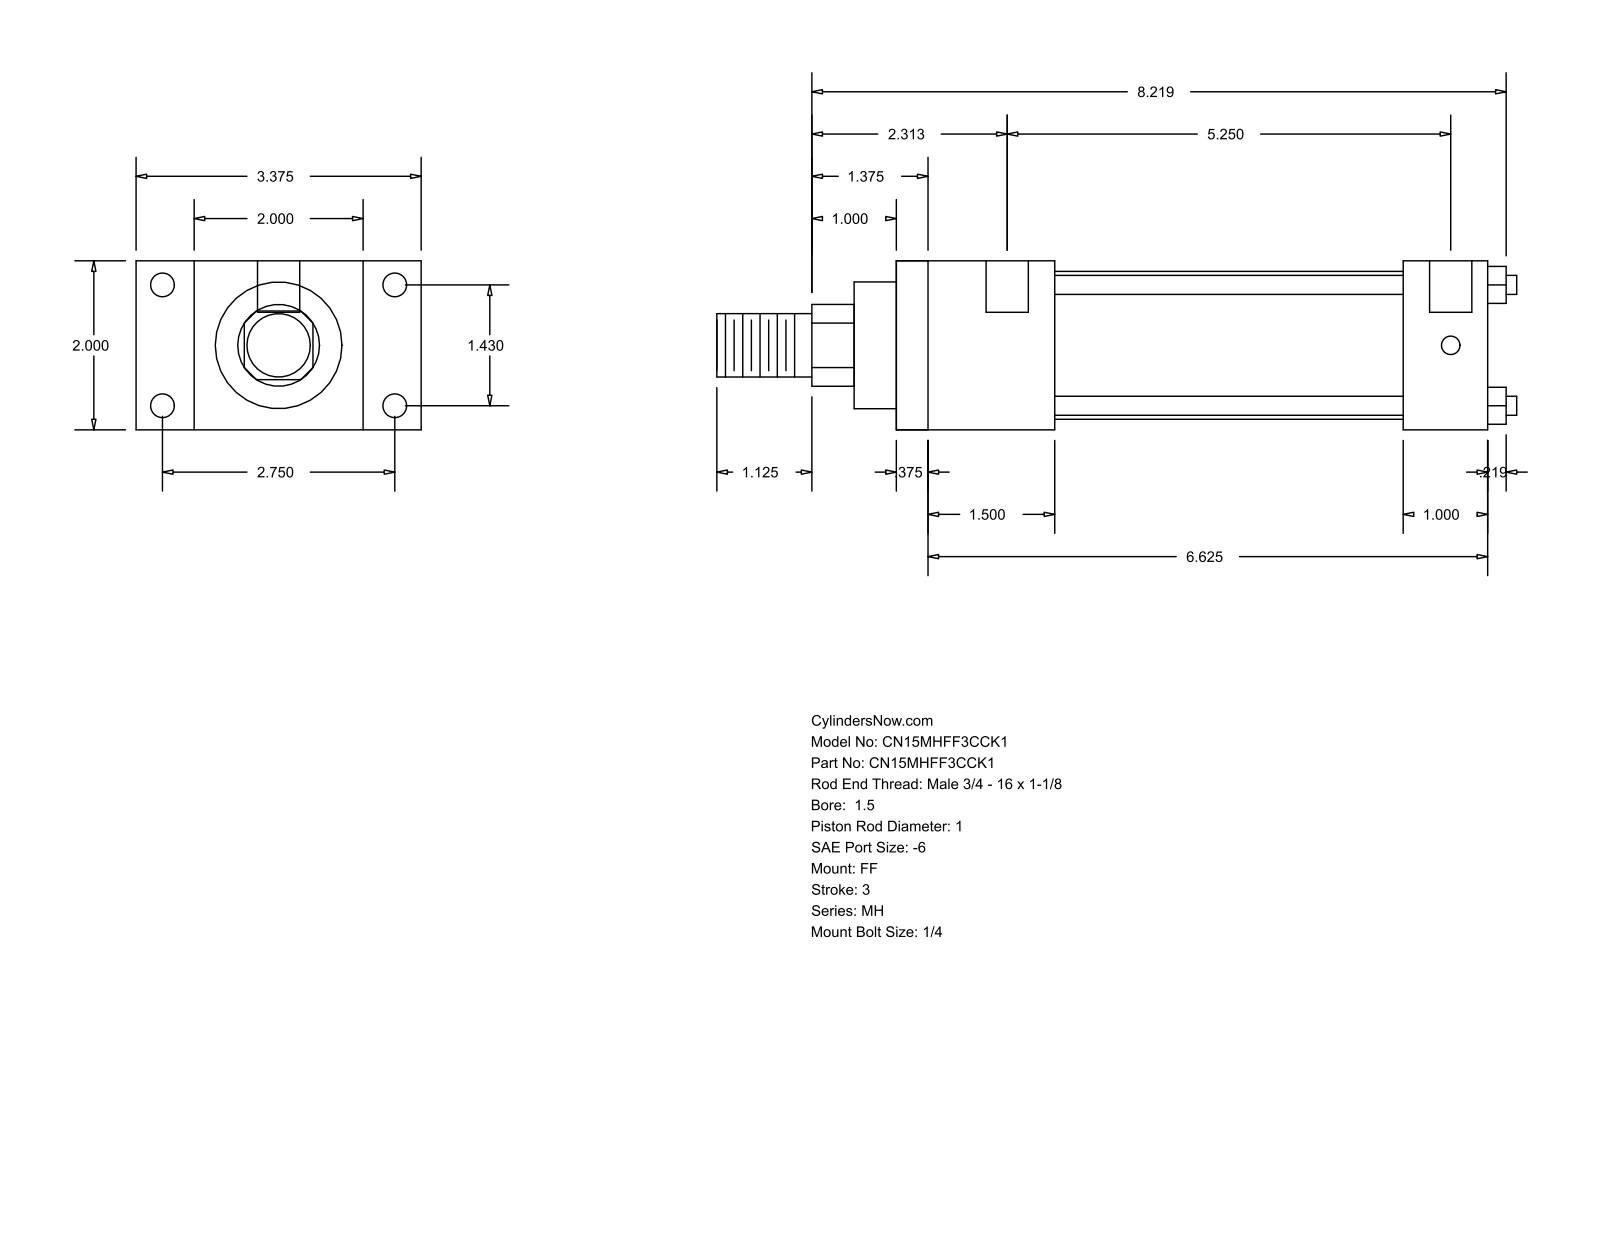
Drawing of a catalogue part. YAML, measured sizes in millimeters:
part_name: "MH_FF__0150_1"
step_written_by: "GSSL Pune (CONFIG_CONTROL_DESIGN)"
units: millimeters
bodies: {solids: 0, faces: 92, planar: 64, cylindrical: 28, other: 0}
overall_size: [240.51, 85.72, 50.8]
round_holes:
  - {diameter: 5.56, count: 4}
  - {diameter: 7.14, count: 4}
  - {diameter: 12.7, count: 2}
round_bosses_or_shafts:
  - {diameter: 5.71, count: 4}
  - {diameter: 44.45, count: 1}
  - {diameter: 38.1, count: 1}
  - {diameter: 25.4, count: 1}
  - {diameter: 19.05, count: 1}
partial_cylinders:
  - {radius: 12.29, count: 1}
face_to_face_distances: [50.8, 177.8, 9.52, 168.28, 25.4, 17.46, 68.26, 47.63, 38.11, 130.17]
hole_center_spacings: [36.32, 69.84, 78.72, 136.53, 3.18, 133.35]
